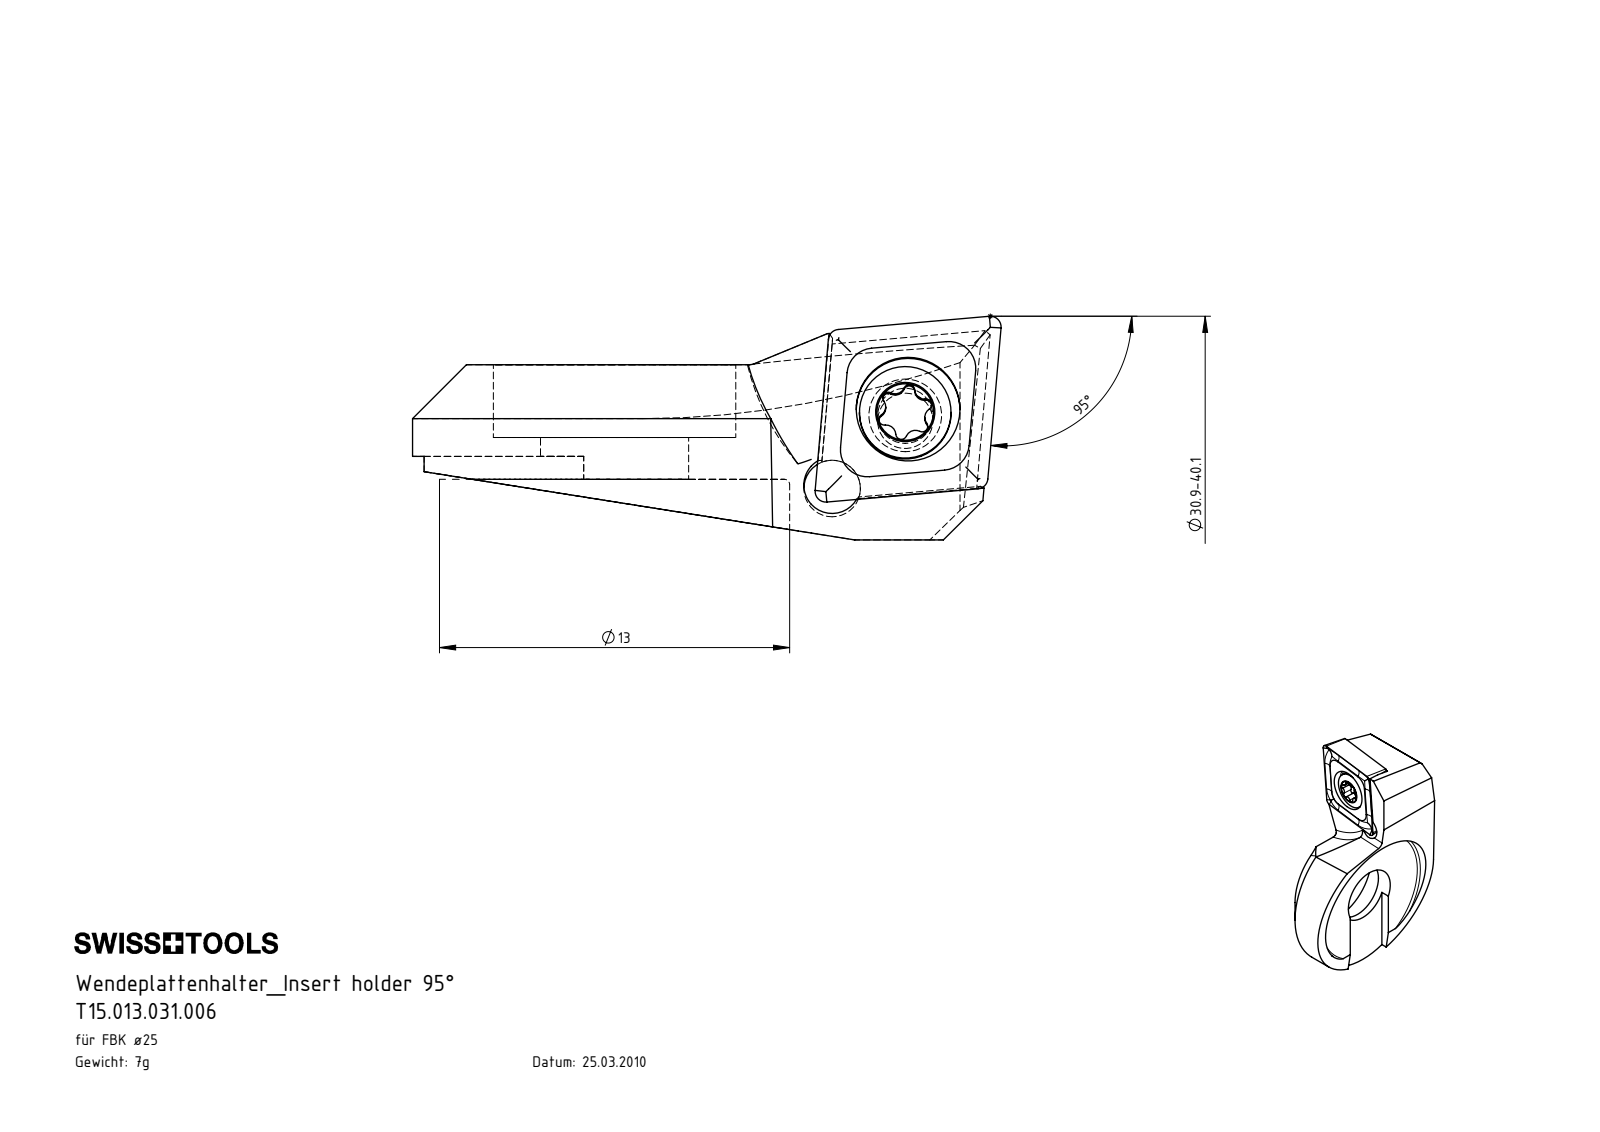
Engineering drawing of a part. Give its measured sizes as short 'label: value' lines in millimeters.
name: F25.WCA.002.006; WCA-ER2.001.006_A; F25-WCA.002.006_D_fertigbearbeitet; CCMT060204
written by: SolidWorks 2017 (AUTOMOTIVE_DESIGN)
unit: mm
bodies: 3 solids, 103 faces (40 planar, 25 cylindrical, 38 other)
size: 21.85 × 15 × 8.3
volume: 784 mm³; area: 1 048 mm²
holes: 1× ⌀2.05, 1× ⌀2.1, 1× ⌀2.8, 1× ⌀3.85, 1× ⌀5.5, 1× ⌀9
bosses: 1× ⌀3.4, 1× ⌀2.5
rounds: 6× R0.21, 5× R0.36, 2× R0.5, 1× R0.36, 1× R6.5, 1× R7.5, 1× R9
face distances: 1.55, 2.7, 4.25, 3.4, 0.7, 0.85, 6.5, 3.8, 3.1, 2.25
hole spacings: 3.84, 3.99
